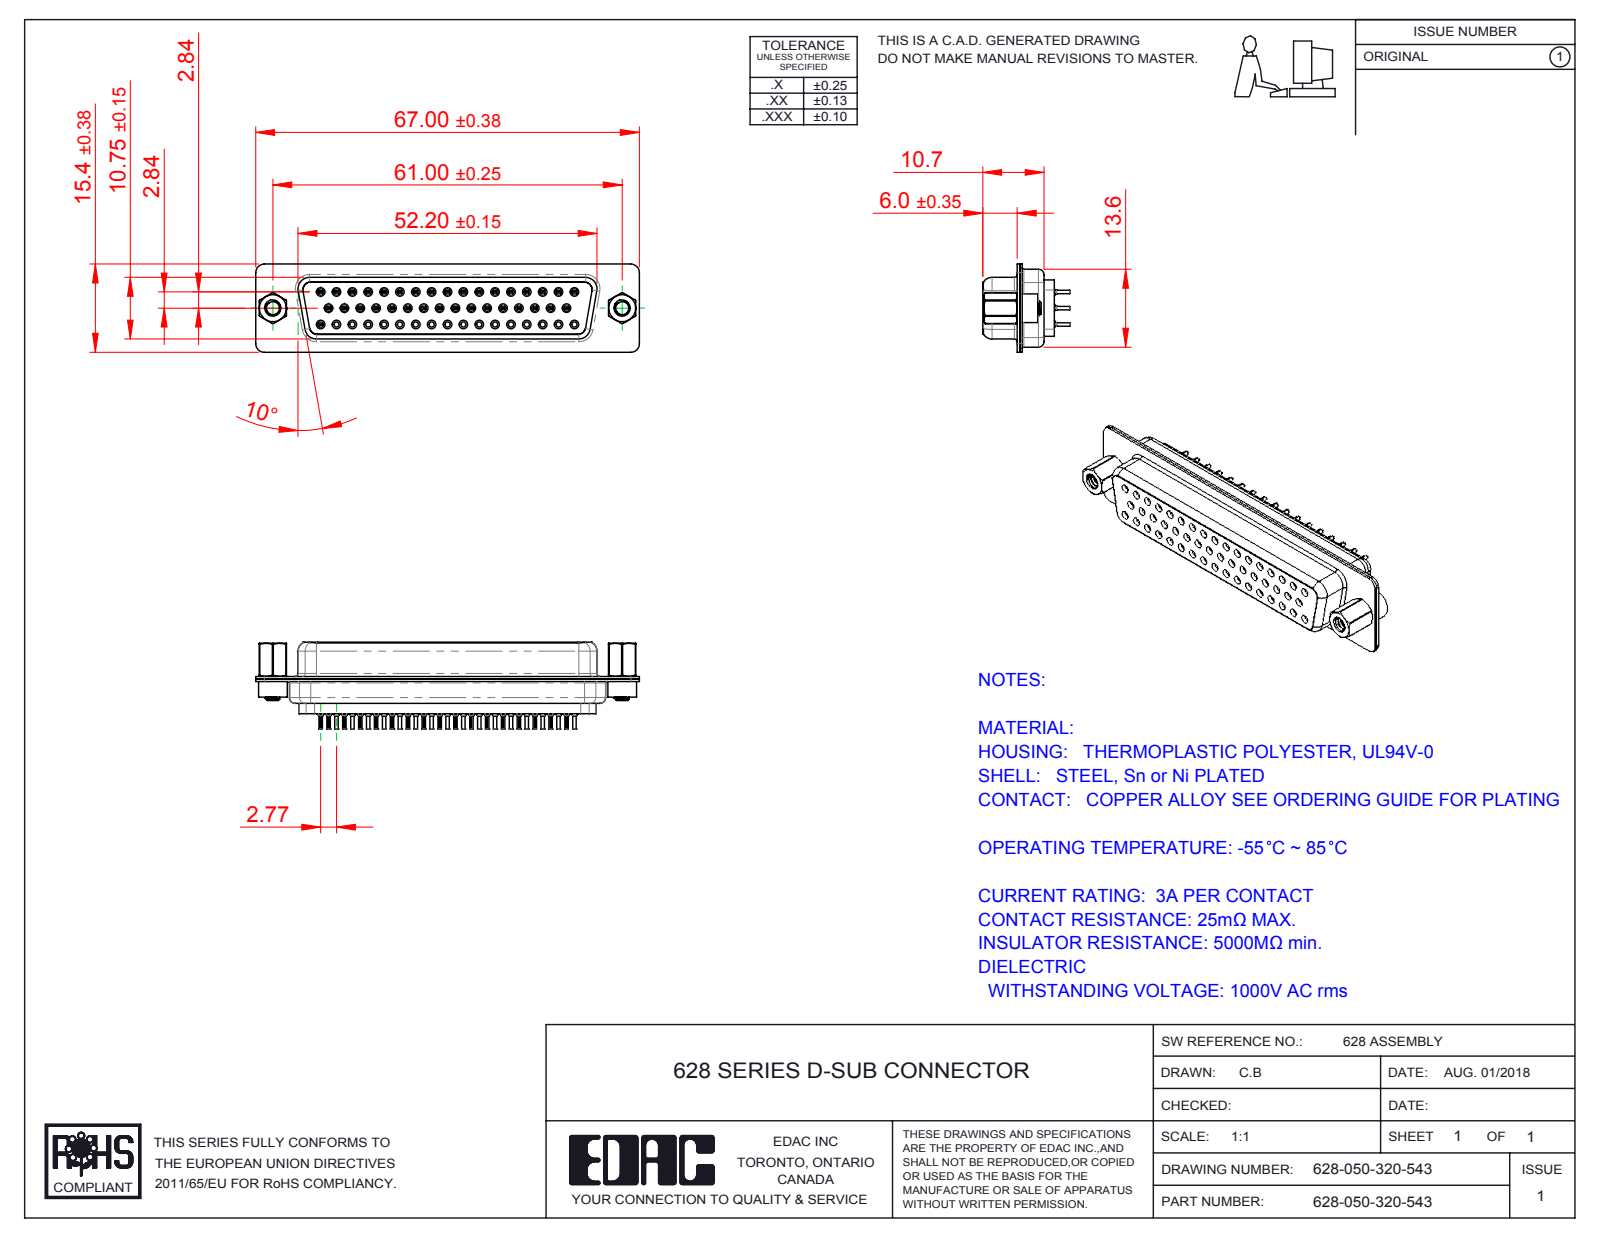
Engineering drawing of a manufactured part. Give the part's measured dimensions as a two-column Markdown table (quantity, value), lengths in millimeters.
| quantity | value |
| --- | --- |
| part name | 628 Shell Front_50 Contacts; 628 4-40 Threaded Rivet; 628 Shell Rear_50 Contacts; 628 Contact Row 2_20L (+5 more) |
| STEP written by | SolidWorks 2016 (CONFIG_CONTROL_DESIGN) |
| units | millimeters |
| bodies | 41 solids, 4931 faces (1191 planar, 1459 cylindrical, 2281 other) |
| overall size | 67 × 15.4 × 15.2 |
| volume | 6 794 mm³ |
| surface area | 14 075 mm² |
| round holes (diameter × count) | 0.9 × 50, 1.6 × 50, 0.2 × 34, 0.8 × 34, 1.1 × 34, 1.7 × 17, 1.5 × 16, 2 × 16, 2.26 × 2, 2.29 × 2, 4 × 2, 4.8 × 2 |
| round bosses / shafts (diameter × count) | 2 × 34, 1.5 × 34, 1.2 × 34, 0.6 × 34, 5 × 2, 4.9 × 2, 2.79 × 2 |
| partial cylindrical surfaces (radius × count) | 0.1 × 68, 0.28 × 33, 1.5 × 16, 2 × 12, 1.35 × 8, 0.25 × 4, 0.5 × 4, 0.6 × 4 |
| main face-to-face distances | 0.45, 0.4, 10.3, 0.9, 6.05, 6.5, 6.45, 6, 12.5, 11.33 |
| hole center spacings | 3.16, 2.77, 5.54, 8.31, 11.08, 13.85, 16.62, 19.39 |
